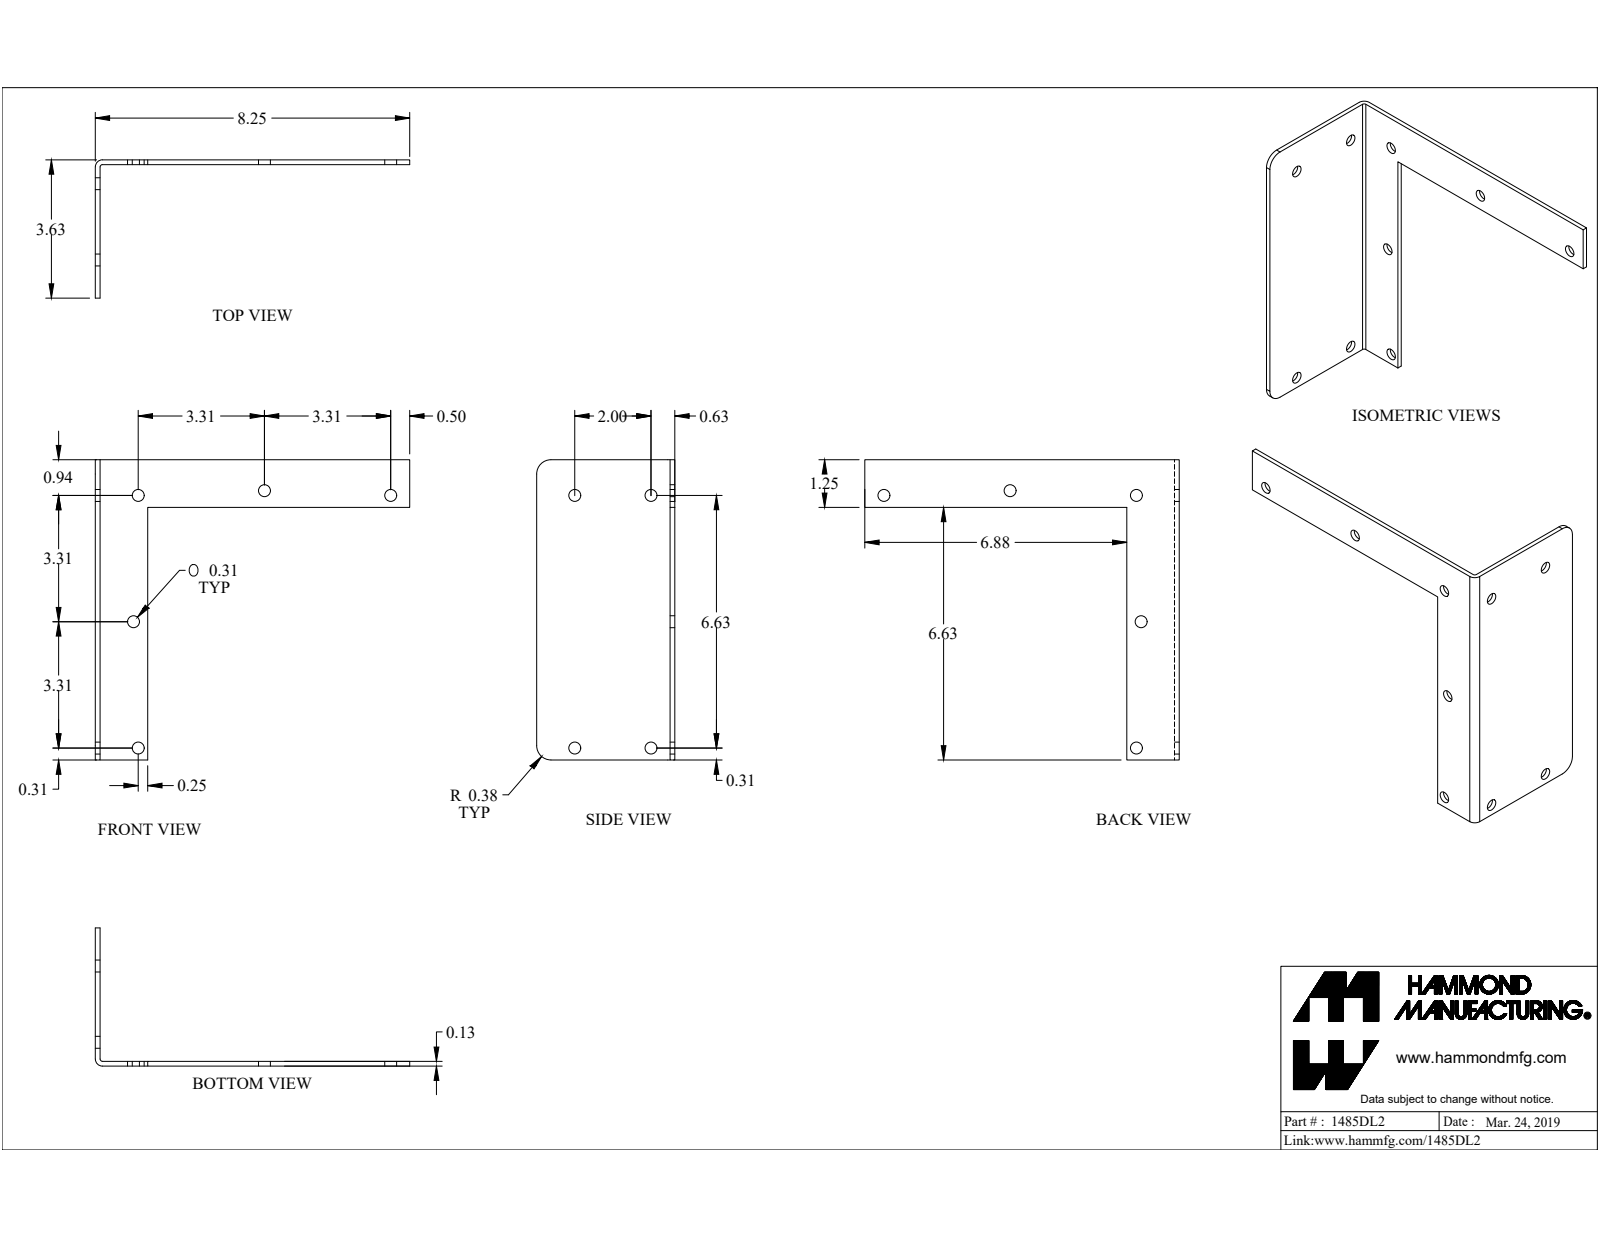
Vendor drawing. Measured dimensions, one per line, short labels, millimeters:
name: 1485DL2
written by: SolidWorks 2019 (CONFIG_CONTROL_DESIGN)
unit: mm
bodies: 1 solid, 23 faces (10 planar, 13 cylindrical, 0 other)
size: 209.6 × 200 × 92.1
volume: 93 850 mm³; area: 62 970 mm²
holes: 9× ⌀8
rounds: 2× R9.5, 1× R1.5, 1× R4.7
face distances: 3.2, 31.8, 88.9, 92.1, 34.9, 200, 168.3, 209.6, 206.4, 174.6
hole spacings: 168.3, 50.8, 84.2, 175.8, 84.2, 84.2, 123.4, 168.3
